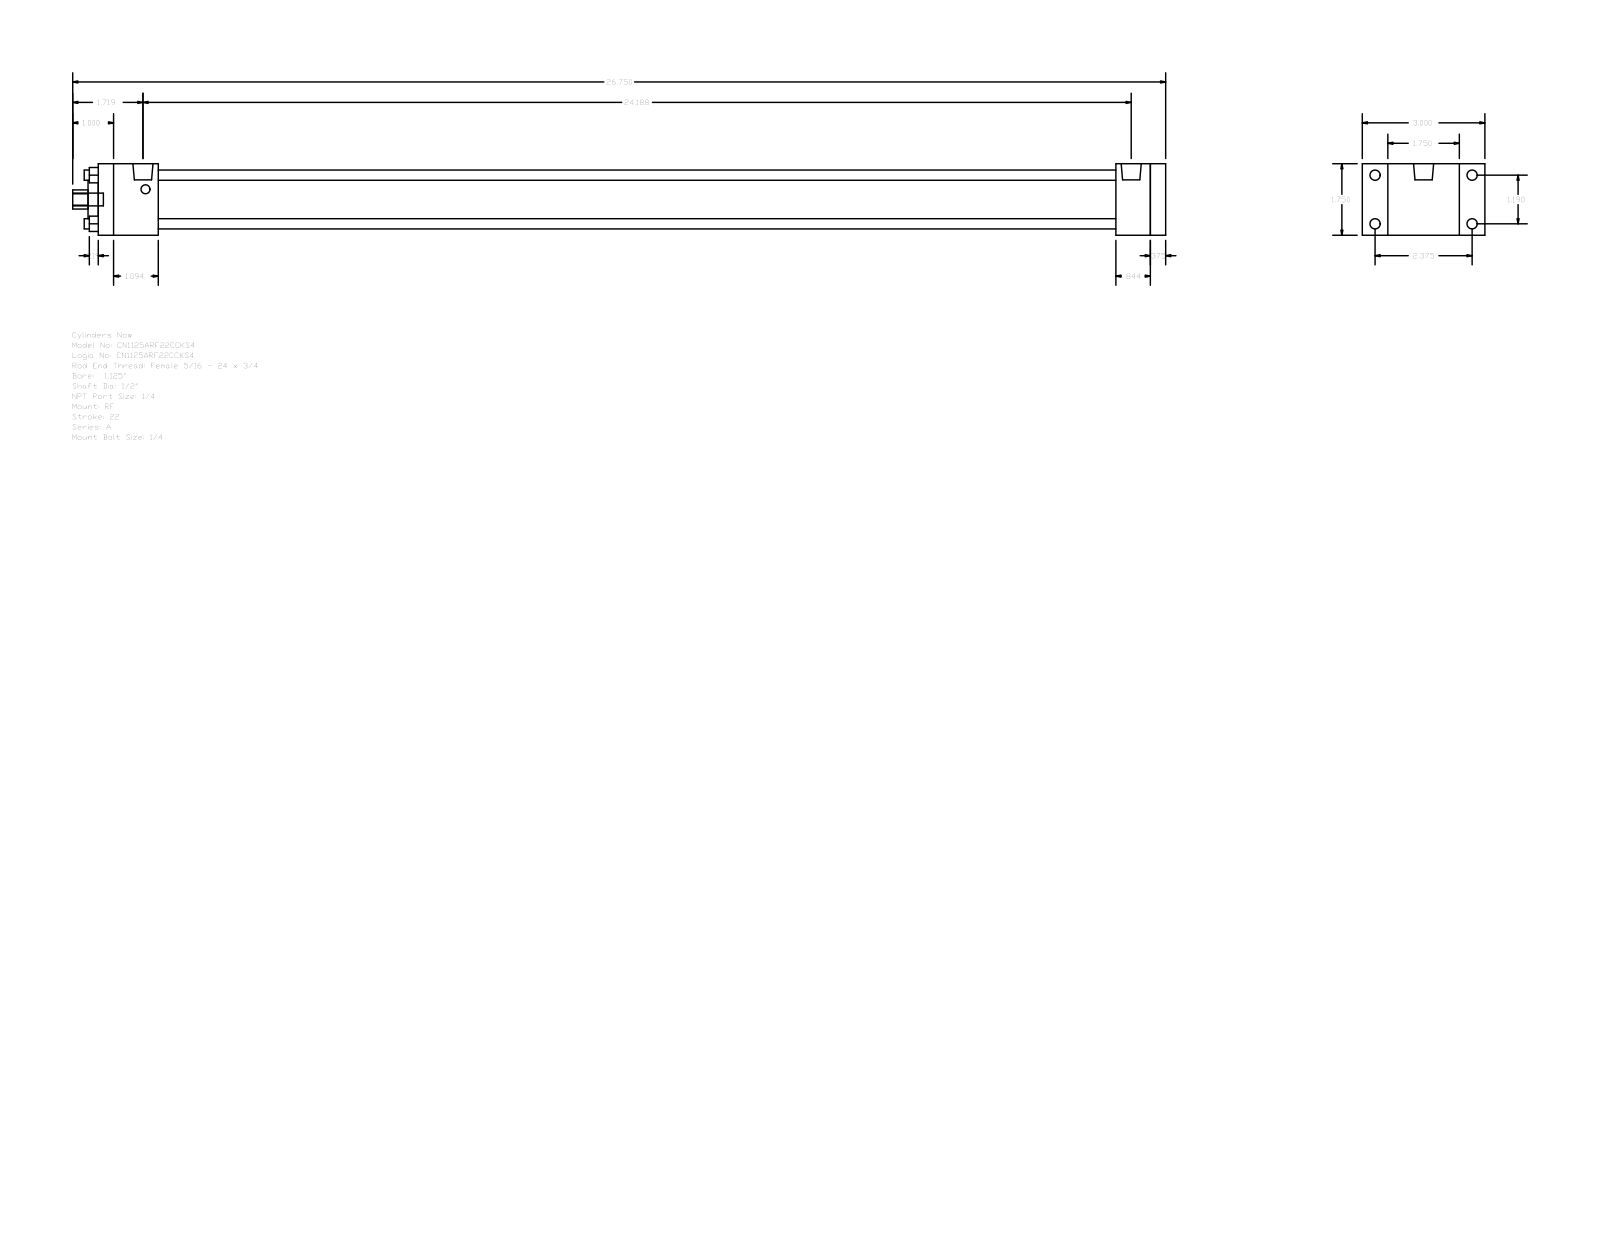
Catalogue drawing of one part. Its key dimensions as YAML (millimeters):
part_name: "A_RF__0112_0.5"
step_written_by: "GSSL Pune (CONFIG_CONTROL_DESIGN)"
units: millimeters
bodies: {solids: 0, faces: 92, planar: 64, cylindrical: 28, other: 0}
overall_size: [679.45, 76.2, 44.45]
round_holes:
  - {diameter: 6.35, count: 4}
  - {diameter: 12.7, count: 1}
  - {diameter: 23.81, count: 1}
  - {diameter: 31.88, count: 1}
round_bosses_or_shafts:
  - {diameter: 6.35, count: 4}
  - {diameter: 5.56, count: 4}
  - {diameter: 12.49, count: 2}
  - {diameter: 7.94, count: 1}
partial_cylinders:
  - {radius: 5.94, count: 1}
face_to_face_distances: [44.46, 9.53, 663.57, 654.04, 37.3, 632.61, 595.31, 616.74, 626.27, 21.43]
hole_center_spacings: [21.37, 30.22, 42.74]
